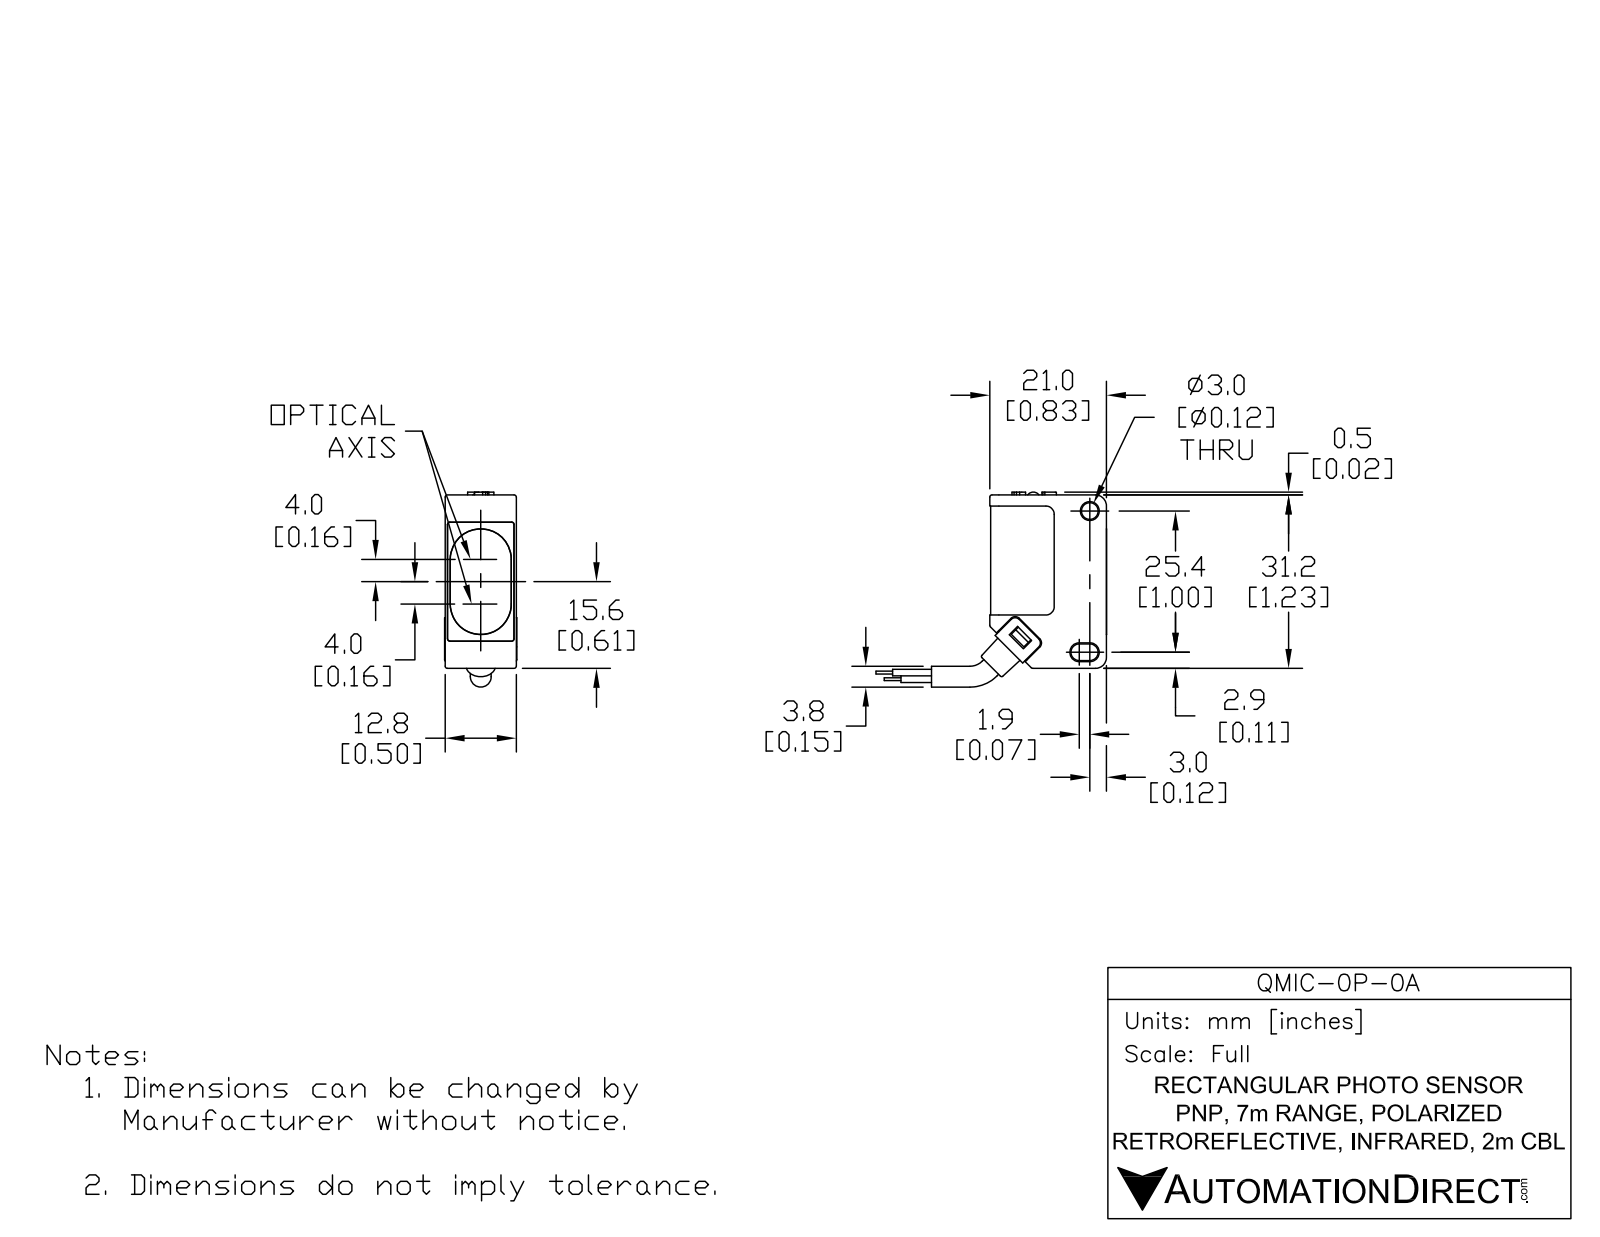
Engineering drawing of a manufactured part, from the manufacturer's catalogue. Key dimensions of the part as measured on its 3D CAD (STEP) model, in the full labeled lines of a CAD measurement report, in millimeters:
Part name (STEP PRODUCT): QMIC-0P-0A
STEP written by: SolidWorks 2017 (AUTOMOTIVE_DESIGN)
Units: millimetres
Bodies: 9 solids, 258 faces (134 planar, 100 cylindrical, 24 other)
Overall size (bounding box): 81.1 × 26.2 × 13
Volume: 7 700 mm³ · Surface area: 5 403 mm²
Round holes (diameter × count): ⌀3 ×3, ⌀3.8 ×1, ⌀5.7 ×1, ⌀7.2 ×1
Round bosses / shafts (diameter × count): ⌀3.5 ×2
Partial cylindrical surfaces — rounded edges, fillets, slot ends (radius × count): R0.4 ×13, R0.5 ×10, R1 ×8, R1.5 ×6, R0.6 ×4, R0.2 ×2, R0.9 ×2, R1.1 ×2
Main face-to-face distances: 0.5, 12.6, 1.5, 0.4, 12.8, 3.5, 12.4, 2, 12.2, 12.5
Hole centre spacings: 5.2
